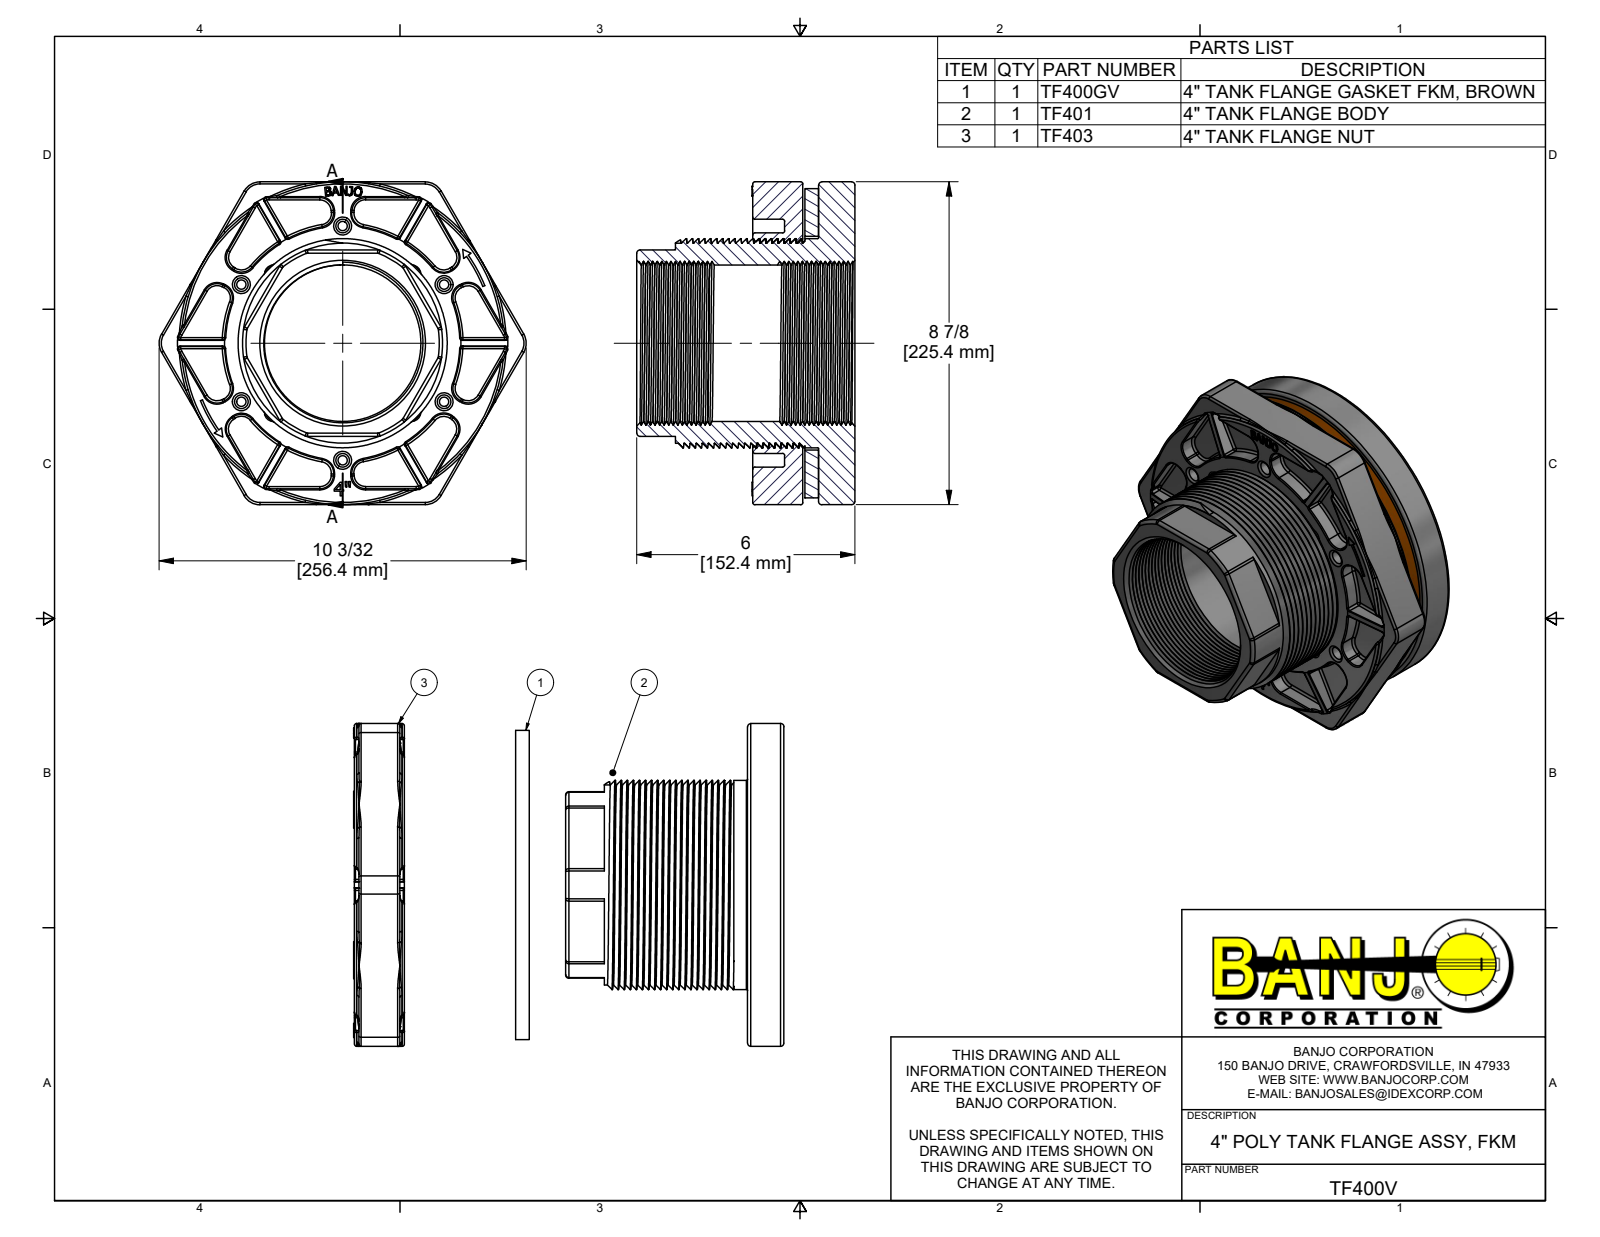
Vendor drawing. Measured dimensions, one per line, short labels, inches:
name: TF400V; TF401; TF403; TF400GV
written by: Autodesk Inventor 2019 (AUTOMOTIVE_DESIGN)
unit: in
bodies: 3 solids, 1803 faces (351 planar, 653 cylindrical, 799 other)
size: 10.093 × 8.875 × 6
volume: 114.9 in³; area: 738.7 in²
holes: 6× ⌀0.375, 1× ⌀4.3, 1× ⌀5.5, 1× ⌀5.875, 1× ⌀7.813
bosses: 1× ⌀8.875, 1× ⌀8.5, 1× ⌀5.75
rounds: 140× R0.06, 62× R0.03, 37× R0.09, 24× R0.015, 24× R0.375, 12× R0.187, 12× R0.5, 8× R0.125
face distances: 0.437, 0.375, 1.375, 1.435, 0.937, 0.219, 0.594, 0.5, 0.781, 1
hole spacings: 3.219, 3.219, 5.575, 5.575, 6.437, 6.438
